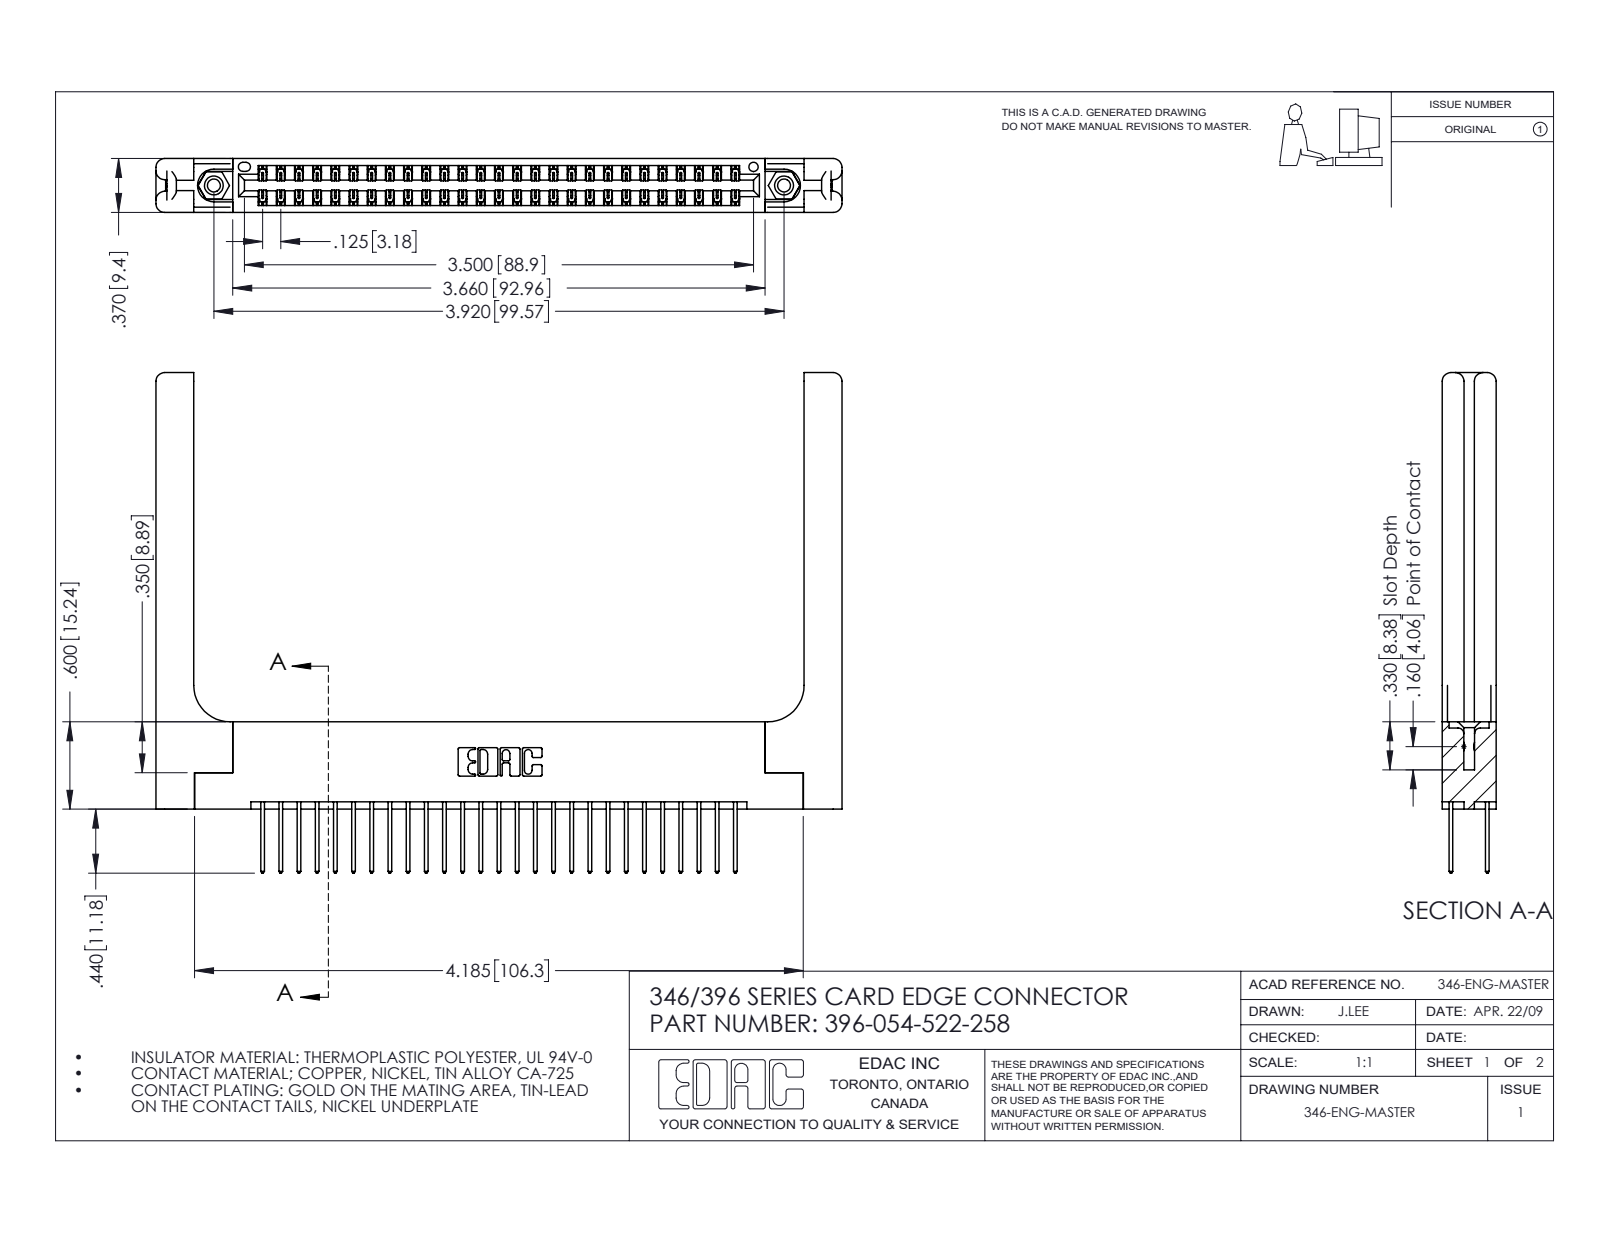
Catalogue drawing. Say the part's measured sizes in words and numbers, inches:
The part is named "345-292-001_345-293-122; 346 Part_Flush Mounting Lugs - 0.156 Dia-TH; 346-220-058_345-220-058; 396-054-522-258 (+1 more)". Its 3-D file was written by "SolidWorks 2016 (CONFIG_CONTROL_DESIGN)". It is 59 solids with 3186 faces: 2114 planar, 1012 cylindrical and 60 other. Overall it measures 4.716 by 3.44 by 0.37 inches. Its volume is 1.171 cubic inches and its surface area 33.27 square inches. Round holes: 2 of diameter 0.089, 2 of diameter 0.125, 2 of diameter 0.156, 1 of diameter 0.064. Round bosses or shafts: 2 of diameter 0.155. Partial cylindrical surfaces (rounded edges, fillets, slot ends): 81 of radius 0.006, 54 of radius 0.01, 22 of radius 0.01, 16 of radius 0.06, 6 of radius 0.007, 6 of radius 0.031, 3 of radius 0.026, 2 of radius 0.014. The main face-to-face distances are 0.37, 0.072, 0.048, 0.322, 0.25, 0.148, 0.15, 0.025, 0.298, 0.275. The hole center spacings are 0.246, 3.712, 3.92.
